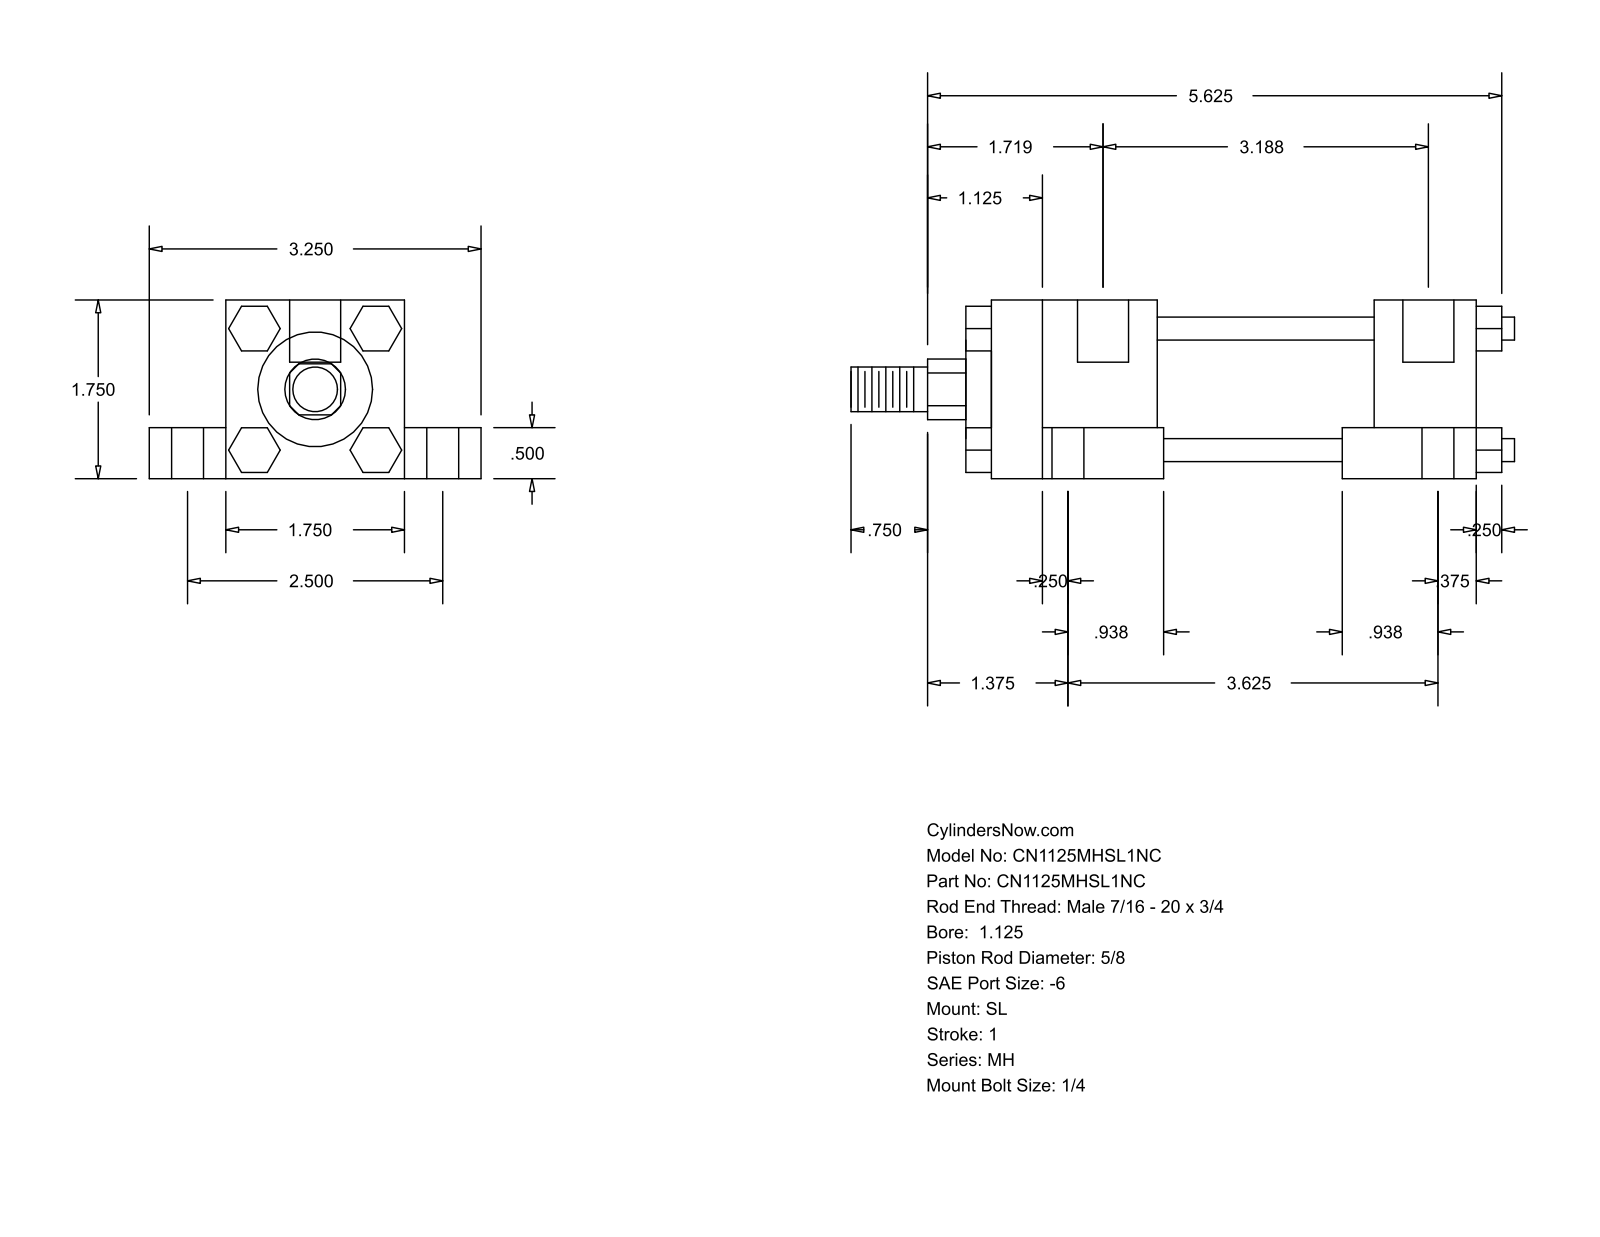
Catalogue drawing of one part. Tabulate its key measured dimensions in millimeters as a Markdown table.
| quantity | value |
| --- | --- |
| part name | MH_SL__0112_0.625 |
| STEP written by | GSSL Pune (CONFIG_CONTROL_DESIGN) |
| units | millimeters |
| bodies | 0 solids, 150 faces (114 planar, 36 cylindrical, 0 other) |
| overall size | 165.1 × 82.55 × 44.45 |
| round holes (diameter × count) | 5.56 × 4, 7.94 × 4, 14.29 × 4, 12.7 × 2 |
| round bosses / shafts (diameter × count) | 5.71 × 4, 34.92 × 1, 28.57 × 1, 15.88 × 1, 11.11 × 1 |
| partial cylindrical surfaces (radius × count) | 7.54 × 1 |
| main face-to-face distances | 44.46, 31.76, 19.04, 12.7, 63.5, 6.35, 127, 11.11, 47.62, 33.34 |
| hole center spacings | 31.84, 32.23, 32.93, 63.5, 77.79, 86.23, 88.9, 89.18 |
